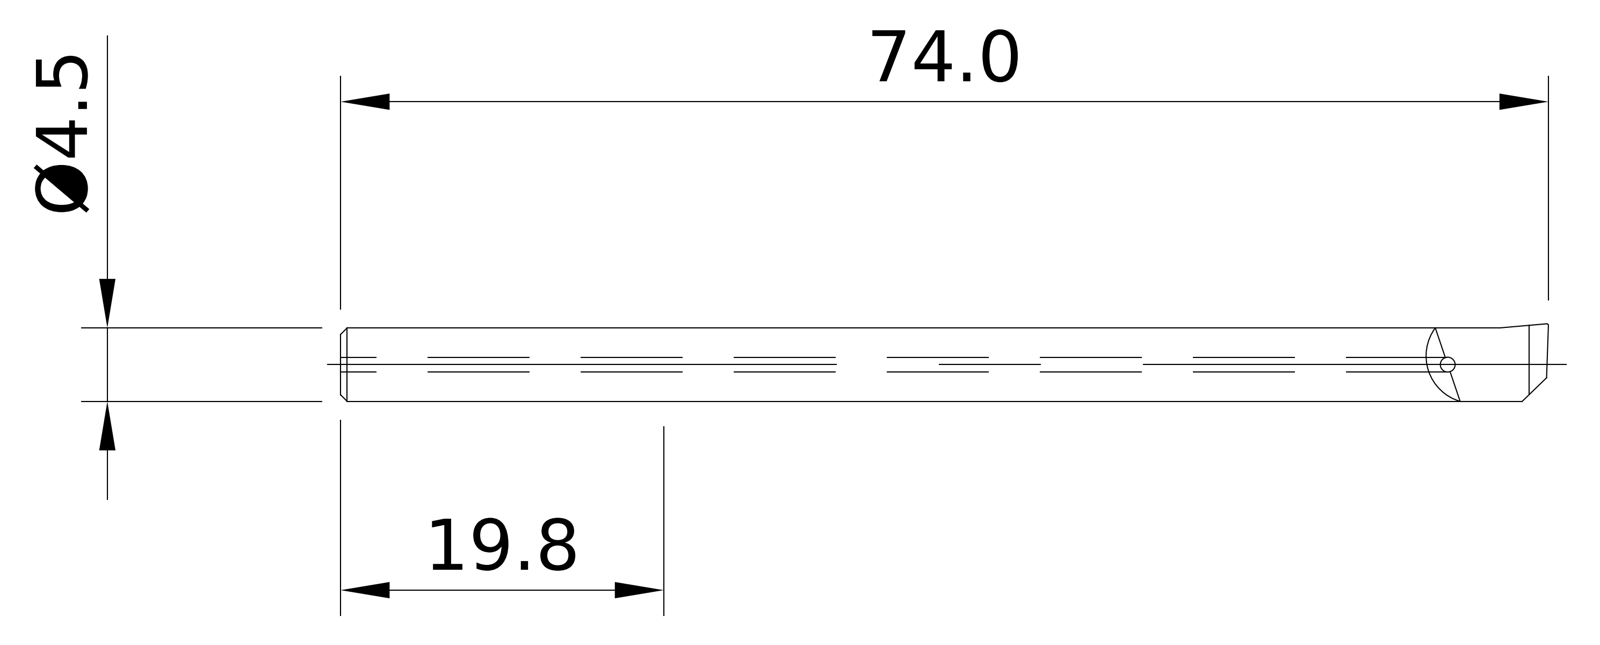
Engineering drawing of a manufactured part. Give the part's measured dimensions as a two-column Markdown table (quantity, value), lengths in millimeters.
| quantity | value |
| --- | --- |
| STEP written by | ACIS (automotive_design) |
| units | millimeters |
| bodies | 1 solid, 19 faces (10 planar, 5 cylindrical, 4 other) |
| overall size | 74 × 4.69 × 4.5 |
| volume | 1 096 mm³ |
| surface area | 1 285 mm² |
| round holes (diameter × count) | 1 × 1 |
| round bosses / shafts (diameter × count) | 4.5 × 1 |
| partial cylindrical surfaces (radius × count) | 0.25 × 1 |
